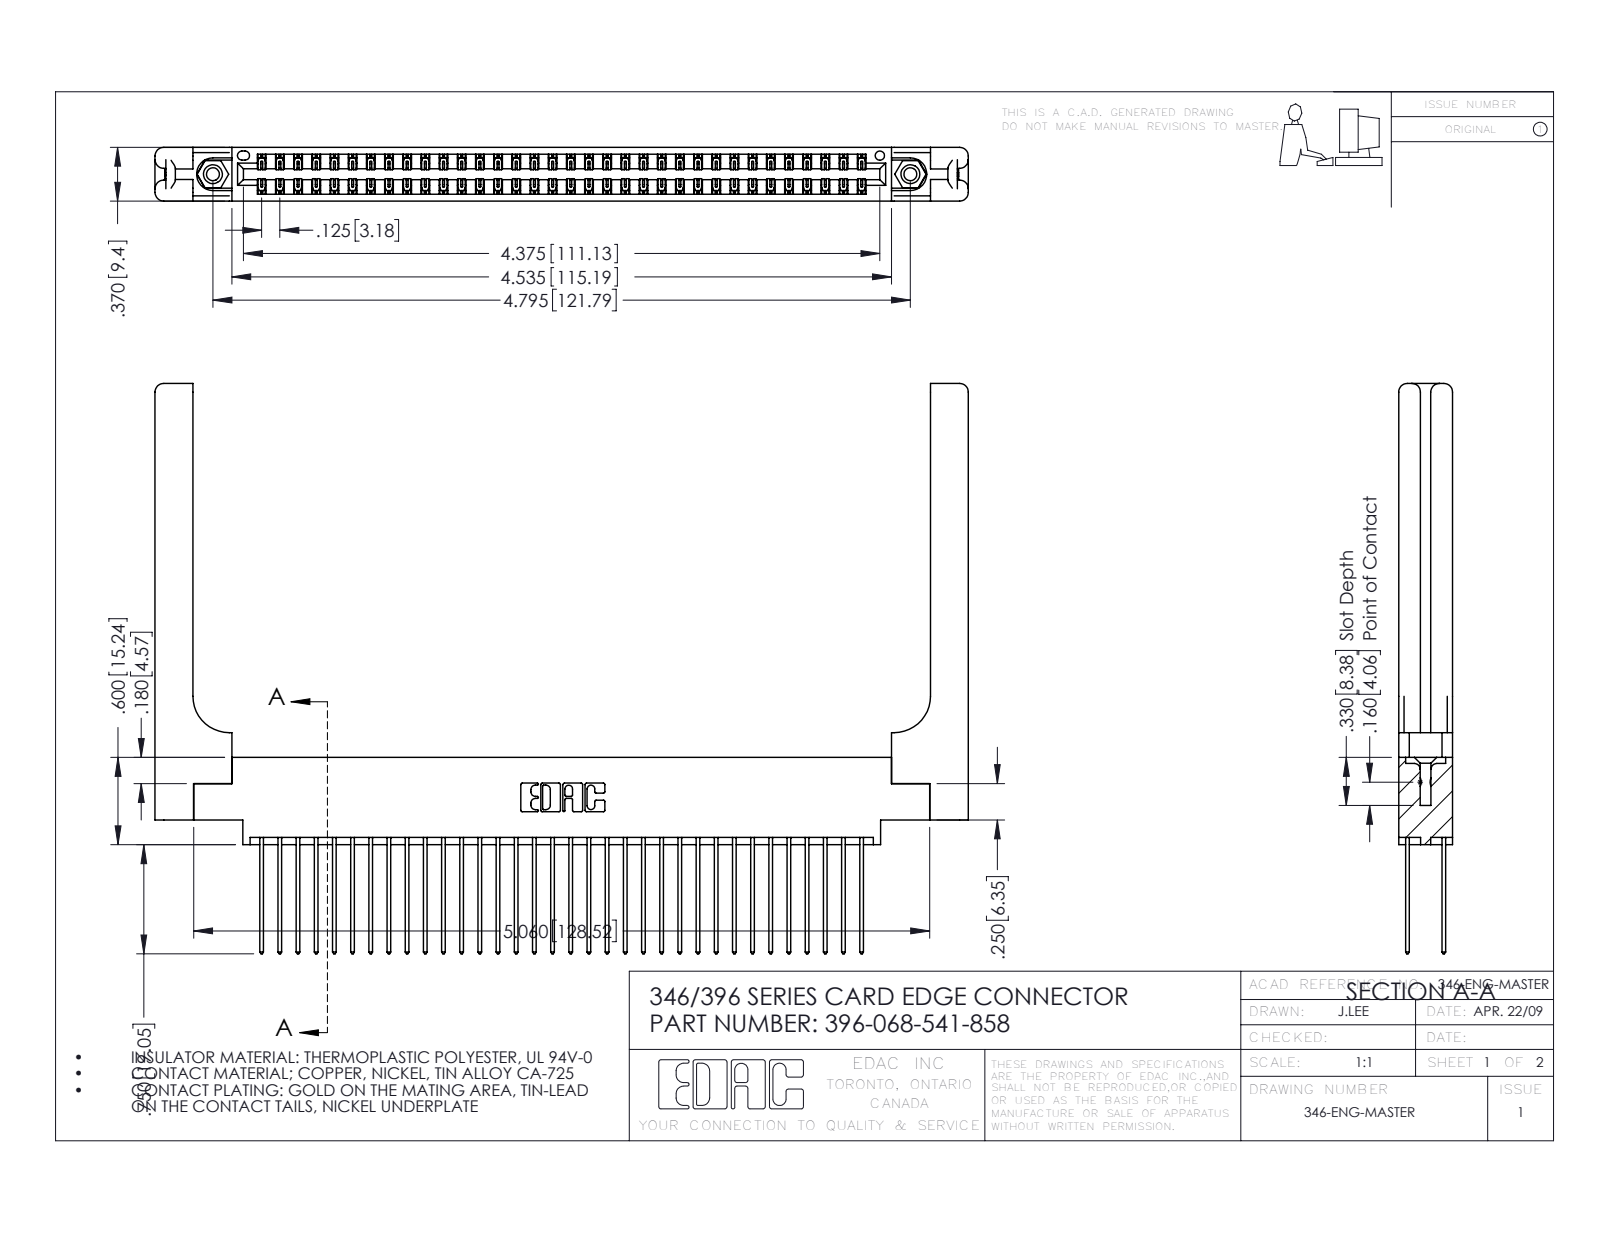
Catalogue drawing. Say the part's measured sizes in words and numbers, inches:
The part is named "345-292-001_345-293-141; 346 Part_0.170 Offset - 0.156 Dia-TH; 346-220-058_345-220-058; 396-068-541-858 (+1 more)". Its 3-D file was written by "SolidWorks 2016 (CONFIG_CONTROL_DESIGN)". It is 73 solids with 3918 faces: 2608 planar, 1250 cylindrical and 60 other. Overall it measures 5.591 by 3.92 by 0.37 inches. Its volume is 1.313 cubic inches and its surface area 40.56 square inches. Round holes: 2 of diameter 0.089, 2 of diameter 0.125, 2 of diameter 0.156, 1 of diameter 0.064. Round bosses or shafts: 2 of diameter 0.155. Partial cylindrical surfaces (rounded edges, fillets, slot ends): 102 of radius 0.006, 68 of radius 0.01, 22 of radius 0.01, 16 of radius 0.06, 6 of radius 0.007, 6 of radius 0.031, 3 of radius 0.026, 2 of radius 0.014. The main face-to-face distances are 0.048, 0.322, 0.072, 0.37, 0.25, 0.025, 0.298, 0.148, 0.15, 0.275. The hole center spacings are 0.246, 4.587, 4.795.
